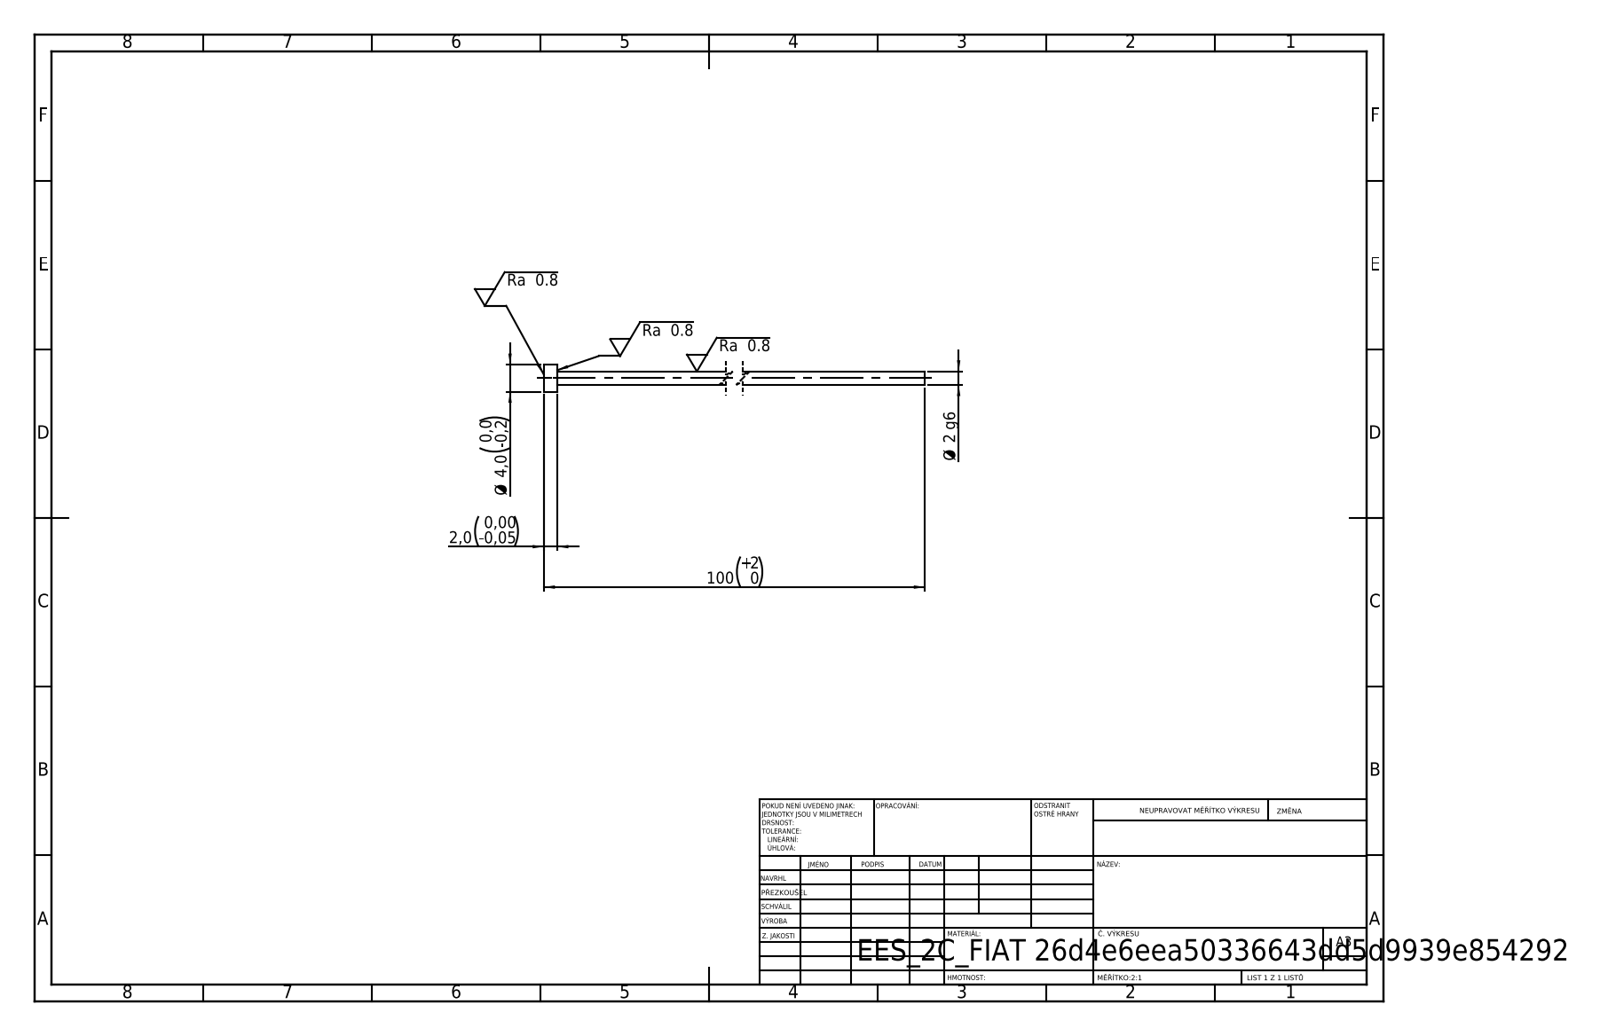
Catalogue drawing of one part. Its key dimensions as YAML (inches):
step_written_by: "SolidWorks 2019 (CONFIG_CONTROL_DESIGN)"
units: inches
bodies: {solids: 1, faces: 7, planar: 3, cylindrical: 4, other: 0}
overall_size: [3.937, 0.157, 0.157]
volume: 0.02
surface_area: 1.03
round_bosses_or_shafts:
  - {diameter: 0.157, count: 1}
  - {diameter: 0.079, count: 1}
face_to_face_distances: [0.079, 3.937, 3.858]
